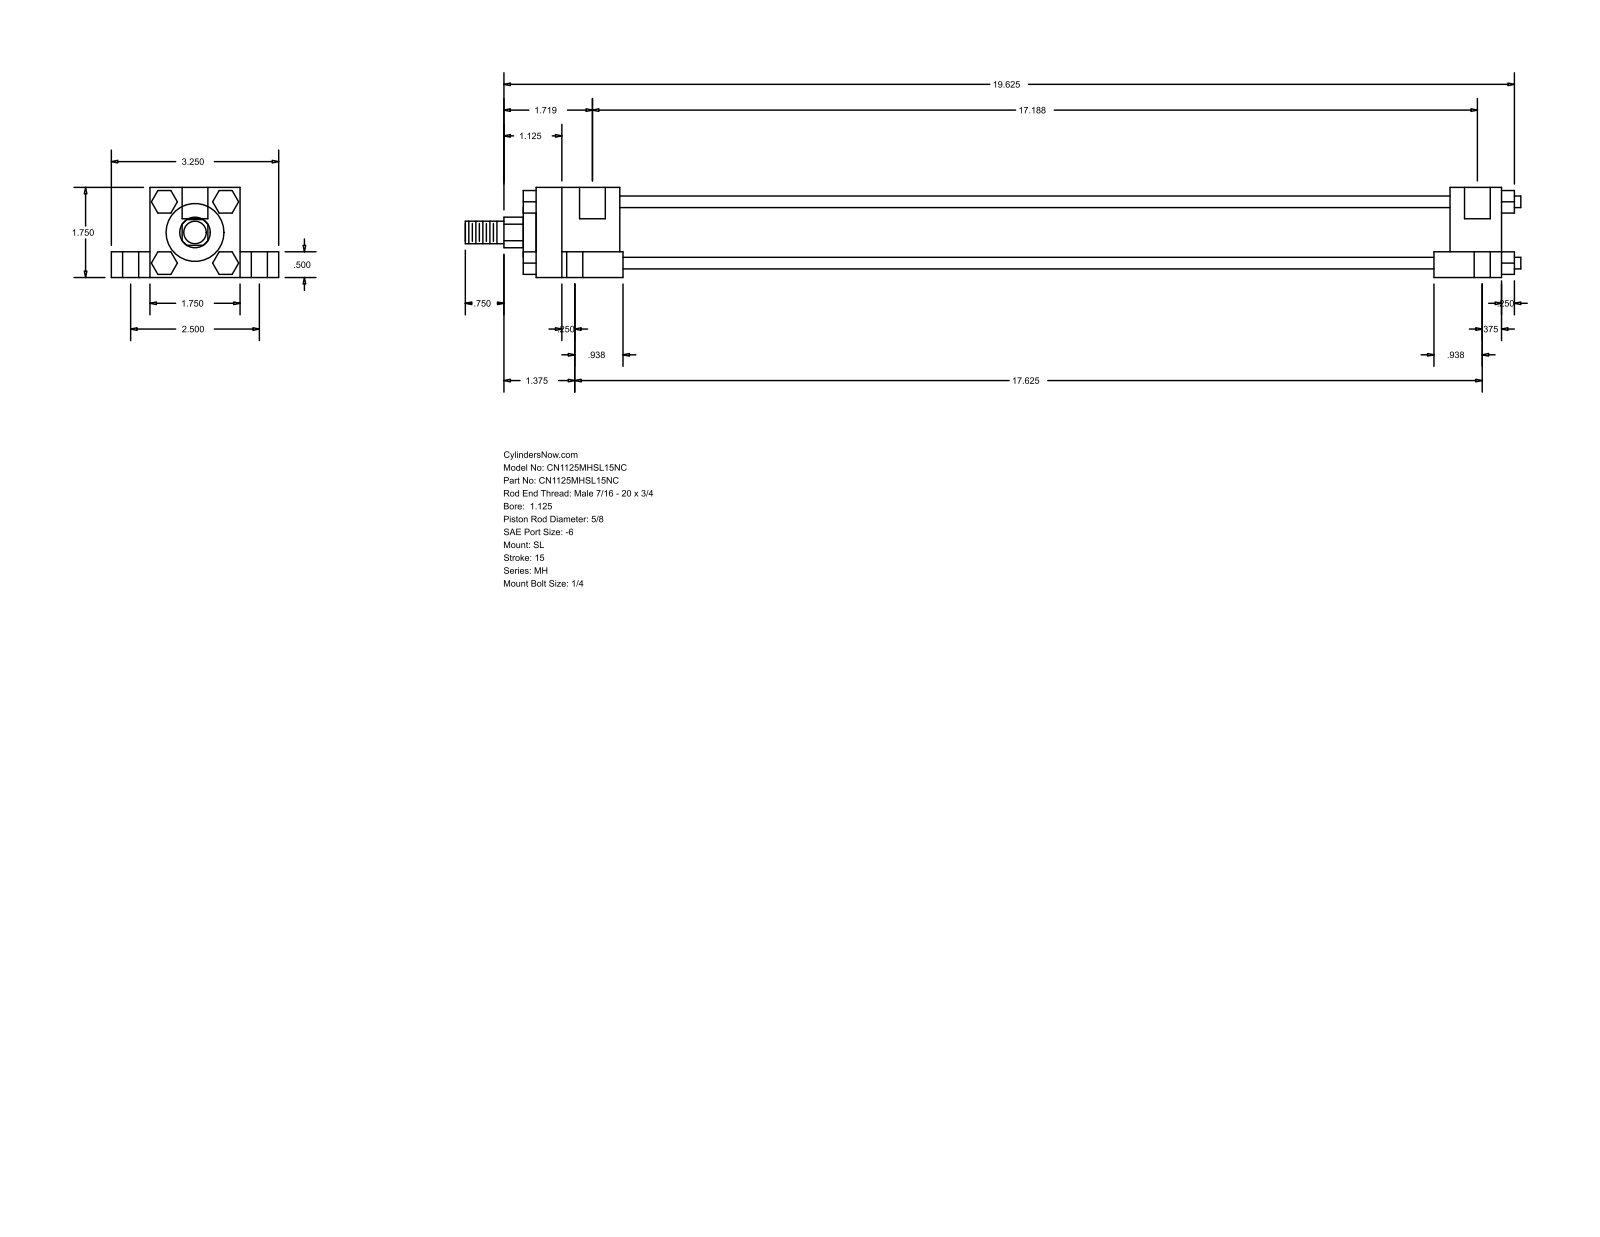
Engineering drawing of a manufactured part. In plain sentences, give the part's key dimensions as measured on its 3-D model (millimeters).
The part is named "MH_SL__0112_0.625". Its 3-D file was written by "GSSL Pune (CONFIG_CONTROL_DESIGN)". It is 0 solids with 150 faces: 114 planar, 36 cylindrical and 0 other. Overall it measures 520.7 by 82.55 by 44.45 millimeters. Round holes: 4 of diameter 5.56, 4 of diameter 7.94, 4 of diameter 14.29, 2 of diameter 12.7. Round bosses or shafts: 4 of diameter 5.71, 1 of diameter 34.92, 1 of diameter 28.57, 1 of diameter 15.88, 1 of diameter 11.11. Partial cylindrical surfaces (rounded edges, fillets, slot ends): 1 of radius 7.54. The main face-to-face distances are 44.46, 19.04, 12.7, 31.76, 63.5, 11.11, 47.62, 409.58, 434.97, 25.39. The hole center spacings are 31.84, 32.23, 32.93, 63.5, 433.39, 436.93, 440.09, 443.26.
